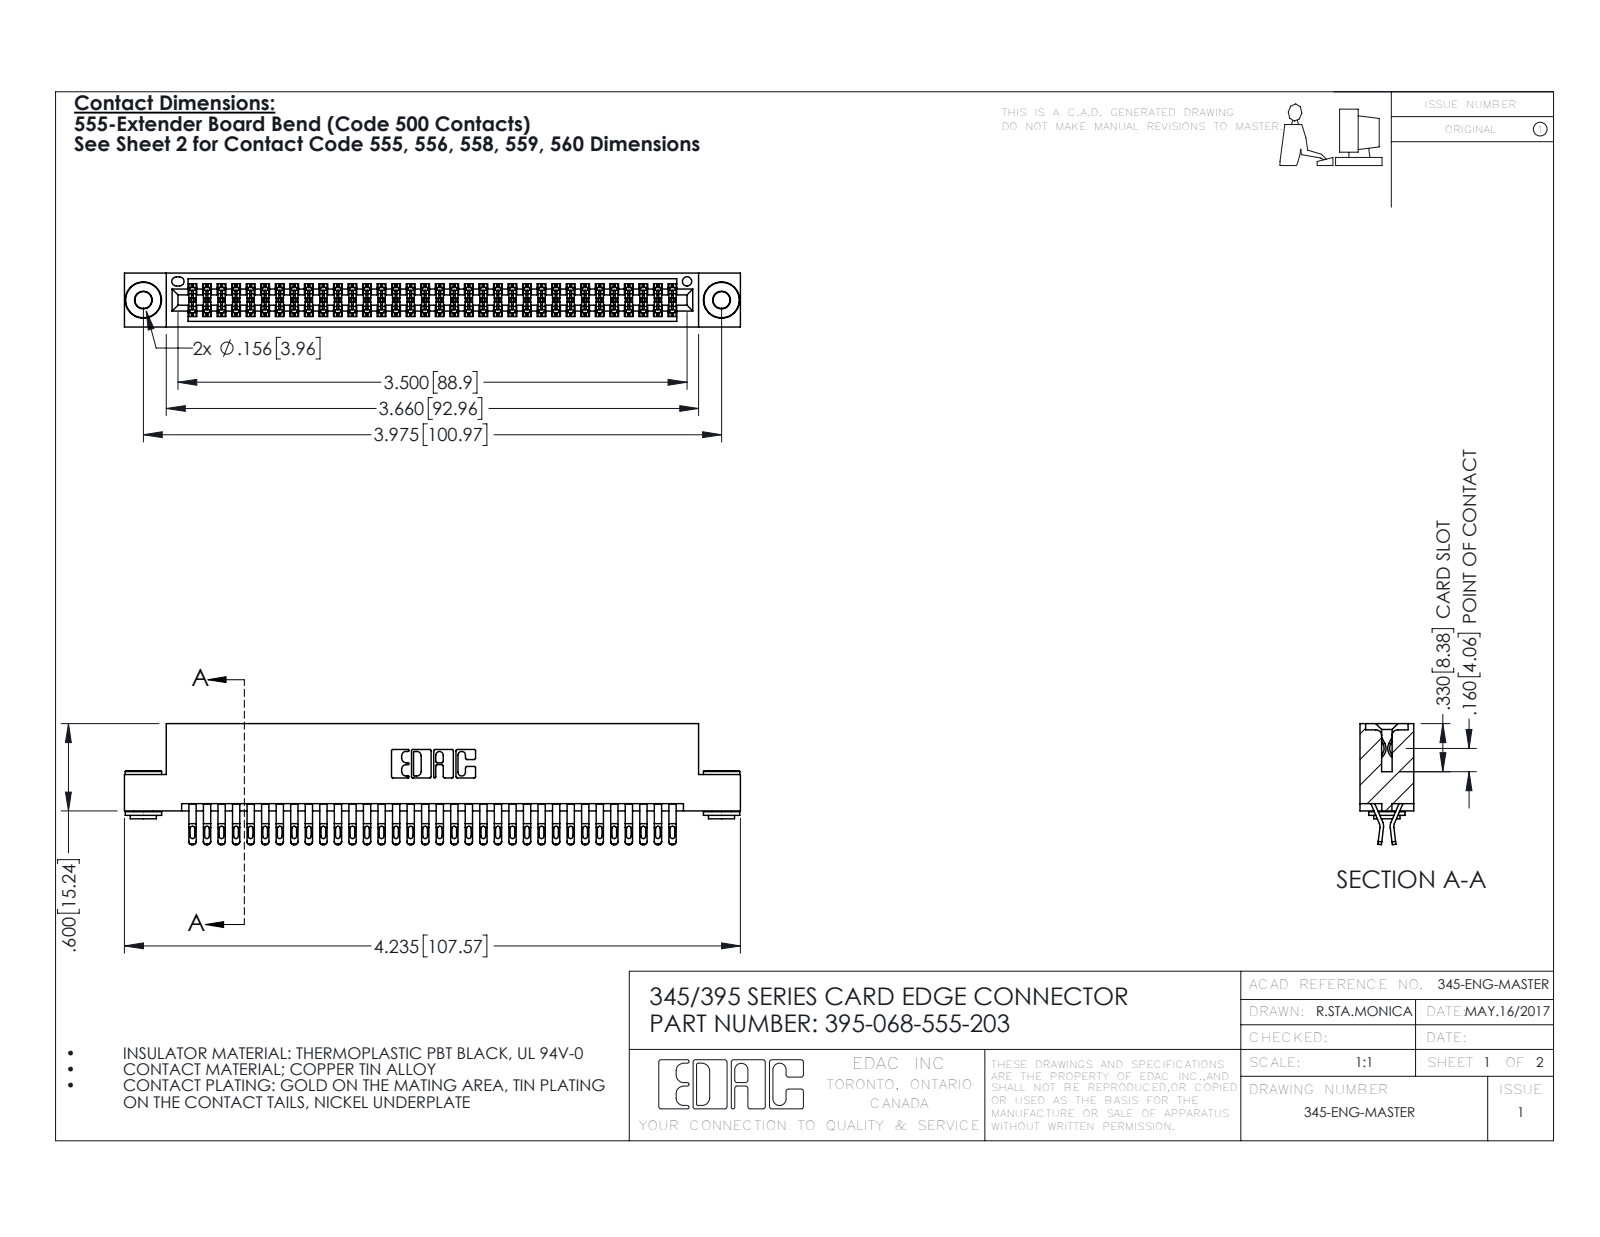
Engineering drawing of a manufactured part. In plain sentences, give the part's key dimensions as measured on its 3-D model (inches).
The part is named "395-068-555-203; 345-250-002_345-250-002-102; 345-292-001_555 Tail; 345 Part_Flush Mounting Lugs - 0.156 Dia-TH". Its 3-D file was written by "SolidWorks 2016 (CONFIG_CONTROL_DESIGN)". It is 71 solids with 3972 faces: 2198 planar, 1766 cylindrical and 8 other. Overall it measures 4.235 by 0.832 by 0.37 inches. Its volume is 0.646 cubic inches and its surface area 25.41 square inches. Round holes: 2 of diameter 0.116, 2 of diameter 0.156, 1 of diameter 0.064. Round bosses or shafts: 2 of diameter 0.25, 2 of diameter 0.18, 2 of diameter 0.136. Partial cylindrical surfaces (rounded edges, fillets, slot ends): 170 of radius 0.016, 136 of radius 0.02, 102 of radius 0.006, 22 of radius 0.01, 6 of radius 0.007, 6 of radius 0.031, 3 of radius 0.026, 2 of radius 0.01. The main face-to-face distances are 0.072, 0.298, 0.2, 0.025, 0.37, 0.098, 0.272, 0.225, 0.175, 0.149. The hole center spacings are 0.27, 3.74, 3.975.
